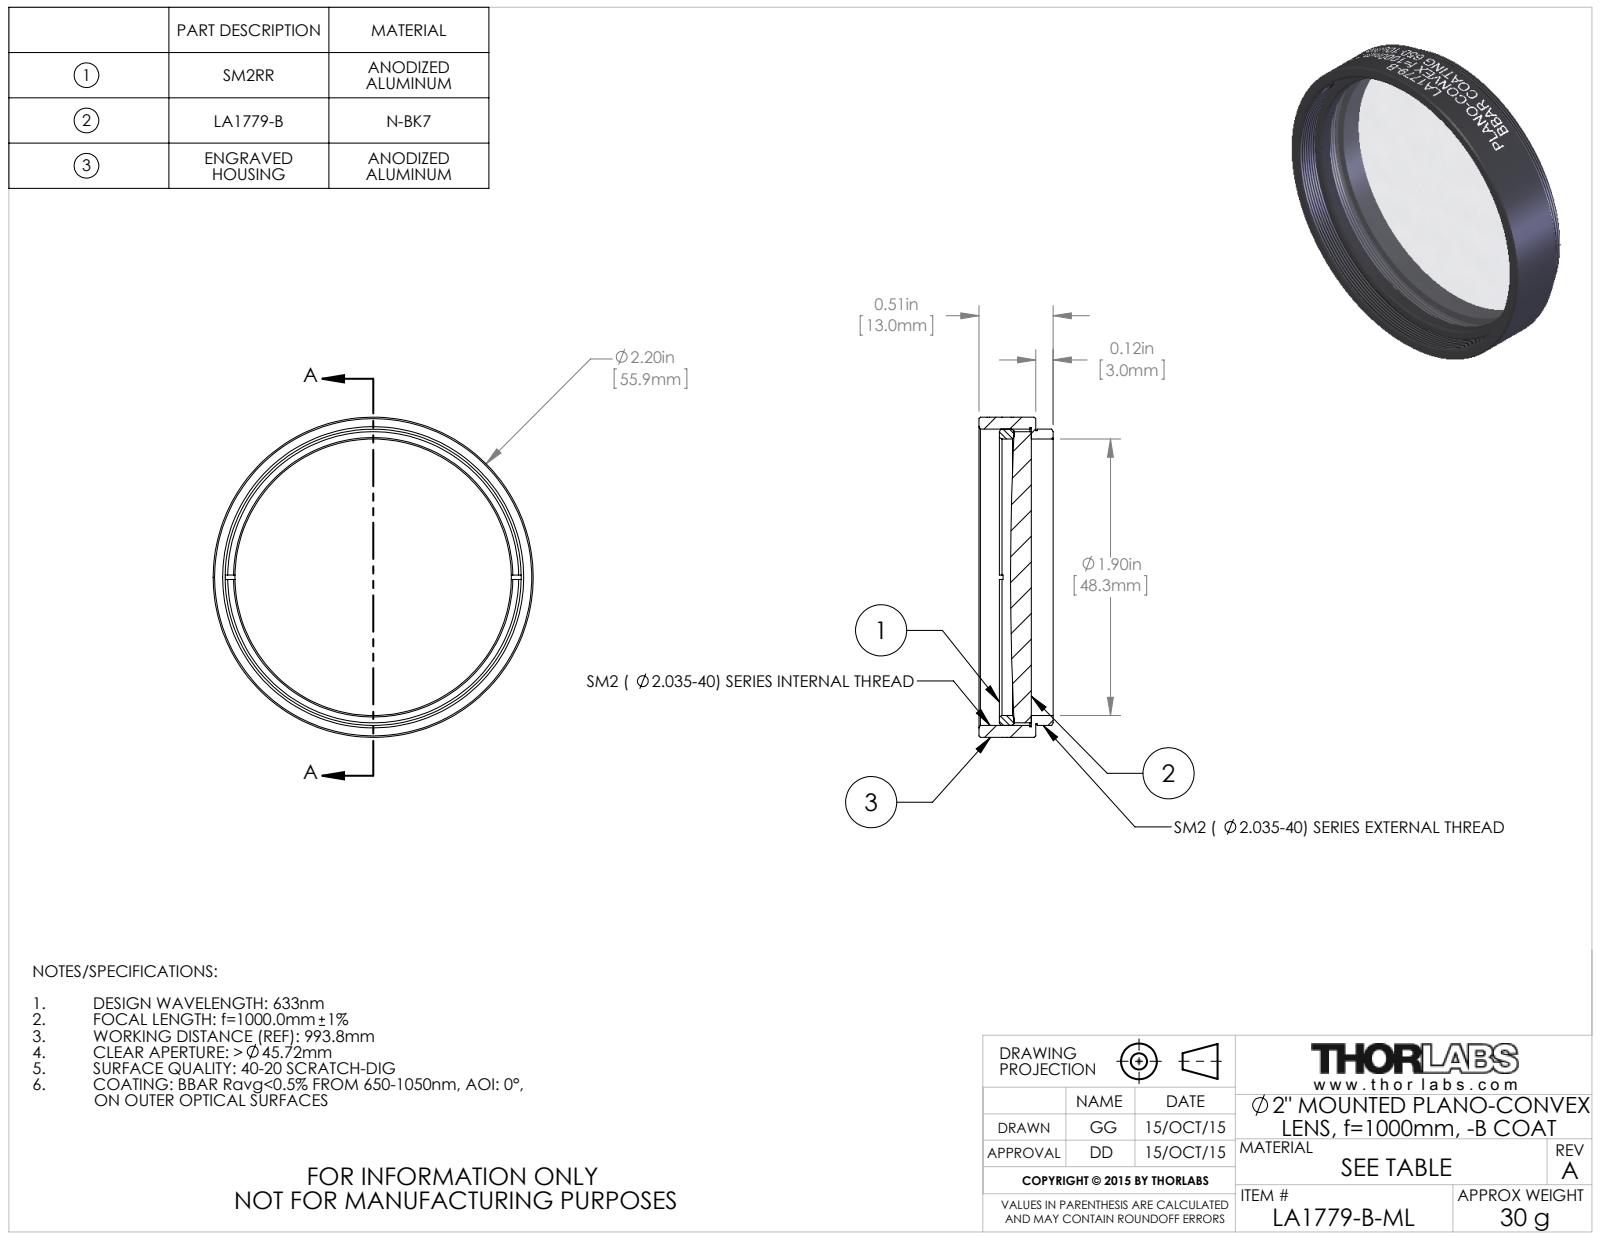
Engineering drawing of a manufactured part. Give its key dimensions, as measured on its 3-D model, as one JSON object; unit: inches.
{"part_name": "TTN039636-E0W", "step_written_by": "SolidWorks 2014 (CONFIG_CONTROL_DESIGN)", "units": "inches", "bodies": {"solids": 3, "faces": 144, "planar": 16, "cylindrical": 108, "other": 20}, "overall_size": [2.2, 2.2, 0.51], "volume_in3": 0.722, "surface_area_in2": 17.59, "round_holes": [[1.9, 1], [2.055, 1]], "round_bosses_or_shafts": [[2.2, 1], [2.035, 1], [2.015, 1], [2, 1]], "face_to_face_distances": [0.03, 0.39, 0.36, 0.12, 0.15, 0.51, 0.27, 0.15, 0.12, 0.241]}
